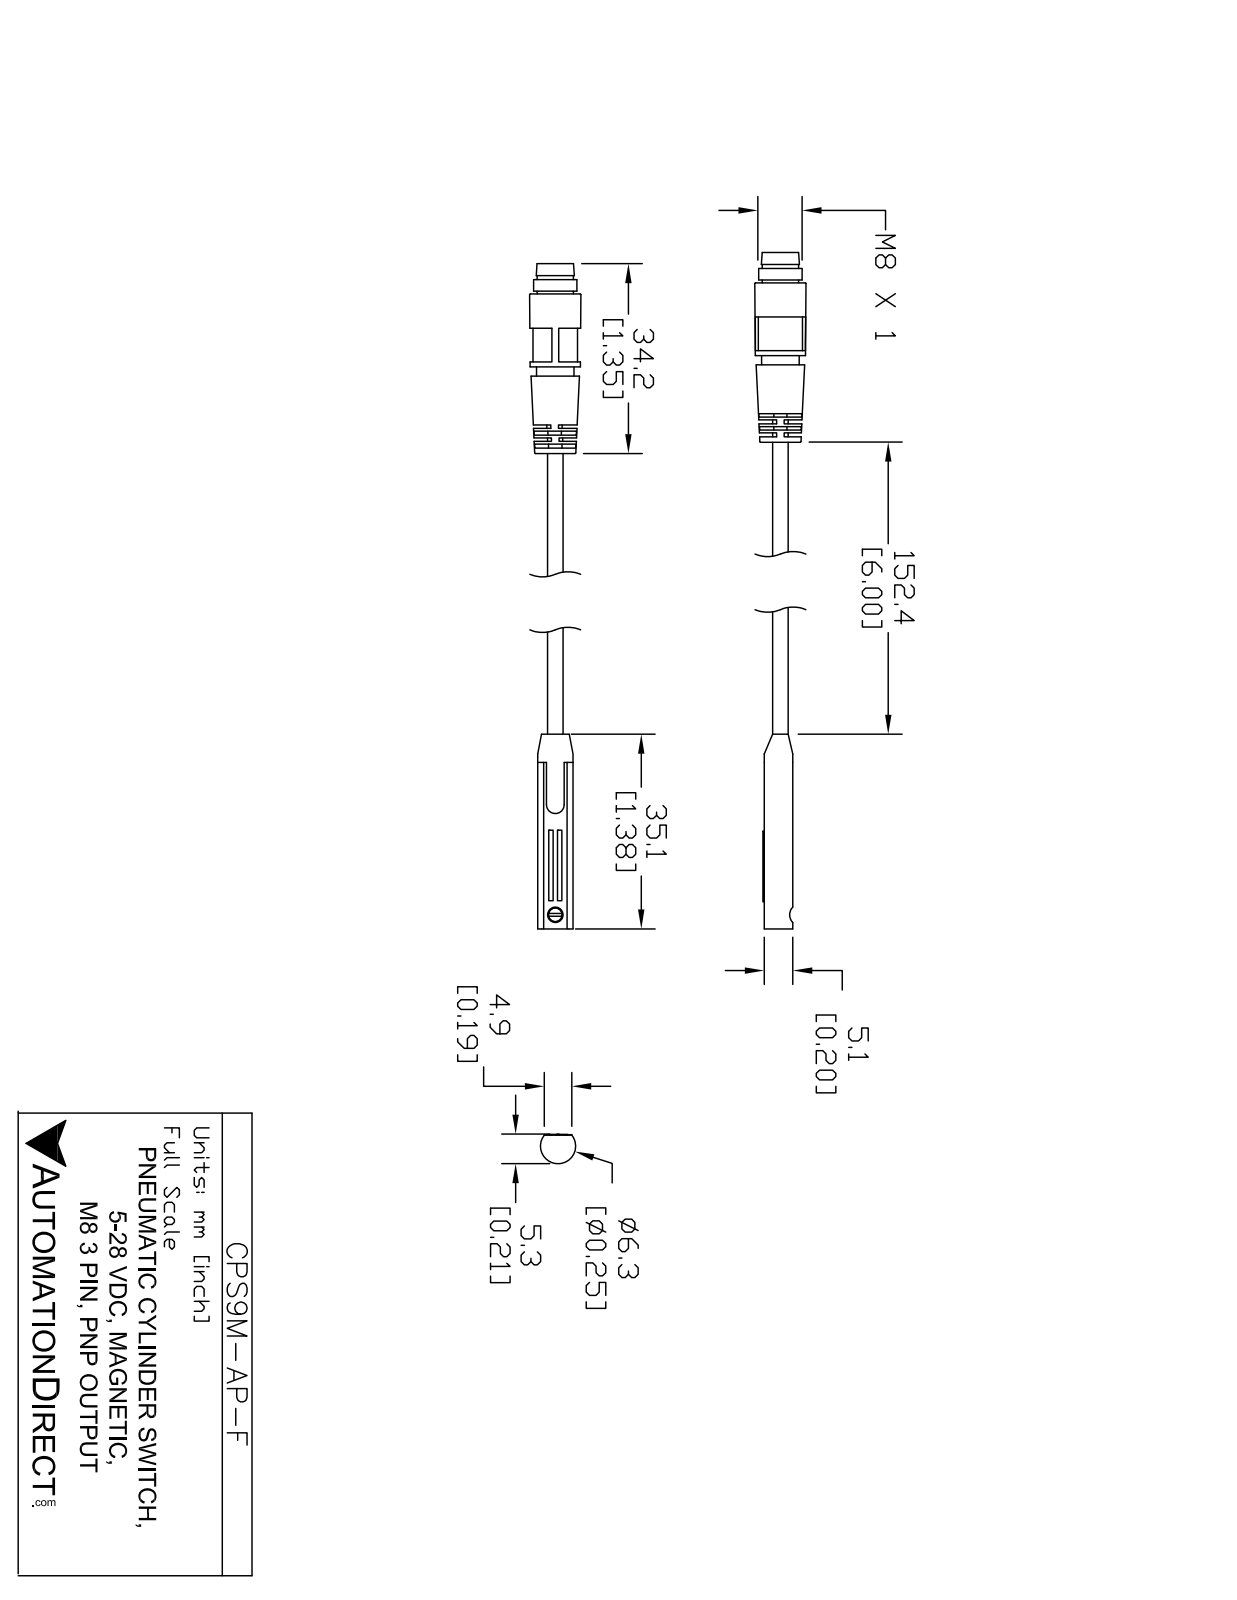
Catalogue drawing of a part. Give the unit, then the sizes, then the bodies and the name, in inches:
Units: inches
Overall size (bounding box): 5.682 × 0.25 × 0.21
Round holes (diameter × count): ⌀0.031 ×1, ⌀0.104 ×1
Round bosses / shafts (diameter × count): ⌀0.138 ×1, ⌀0.105 ×1
Partial cylindrical surfaces — rounded edges, fillets, slot ends (radius × count): R0.005 ×13, R0.015 ×3, R0.031 ×2, R0.045 ×1, R0.062 ×1, R0.105 ×1, R0.125 ×1
Main face-to-face distances: 0.168, 0.02, 0.021, 0.146, 0.062, 0.042, 0.029, 0.071, 0.091, 1.18
Hole centre spacings: 0.136
Volume: 0.075 in³ · Surface area: 3.88 in²
Bodies: 4 solids, 122 faces (48 planar, 50 cylindrical, 24 other)
Part name (STEP PRODUCT): CPS9M-AP-F
STEP written by: SolidWorks 2017 (AUTOMOTIVE_DESIGN)
